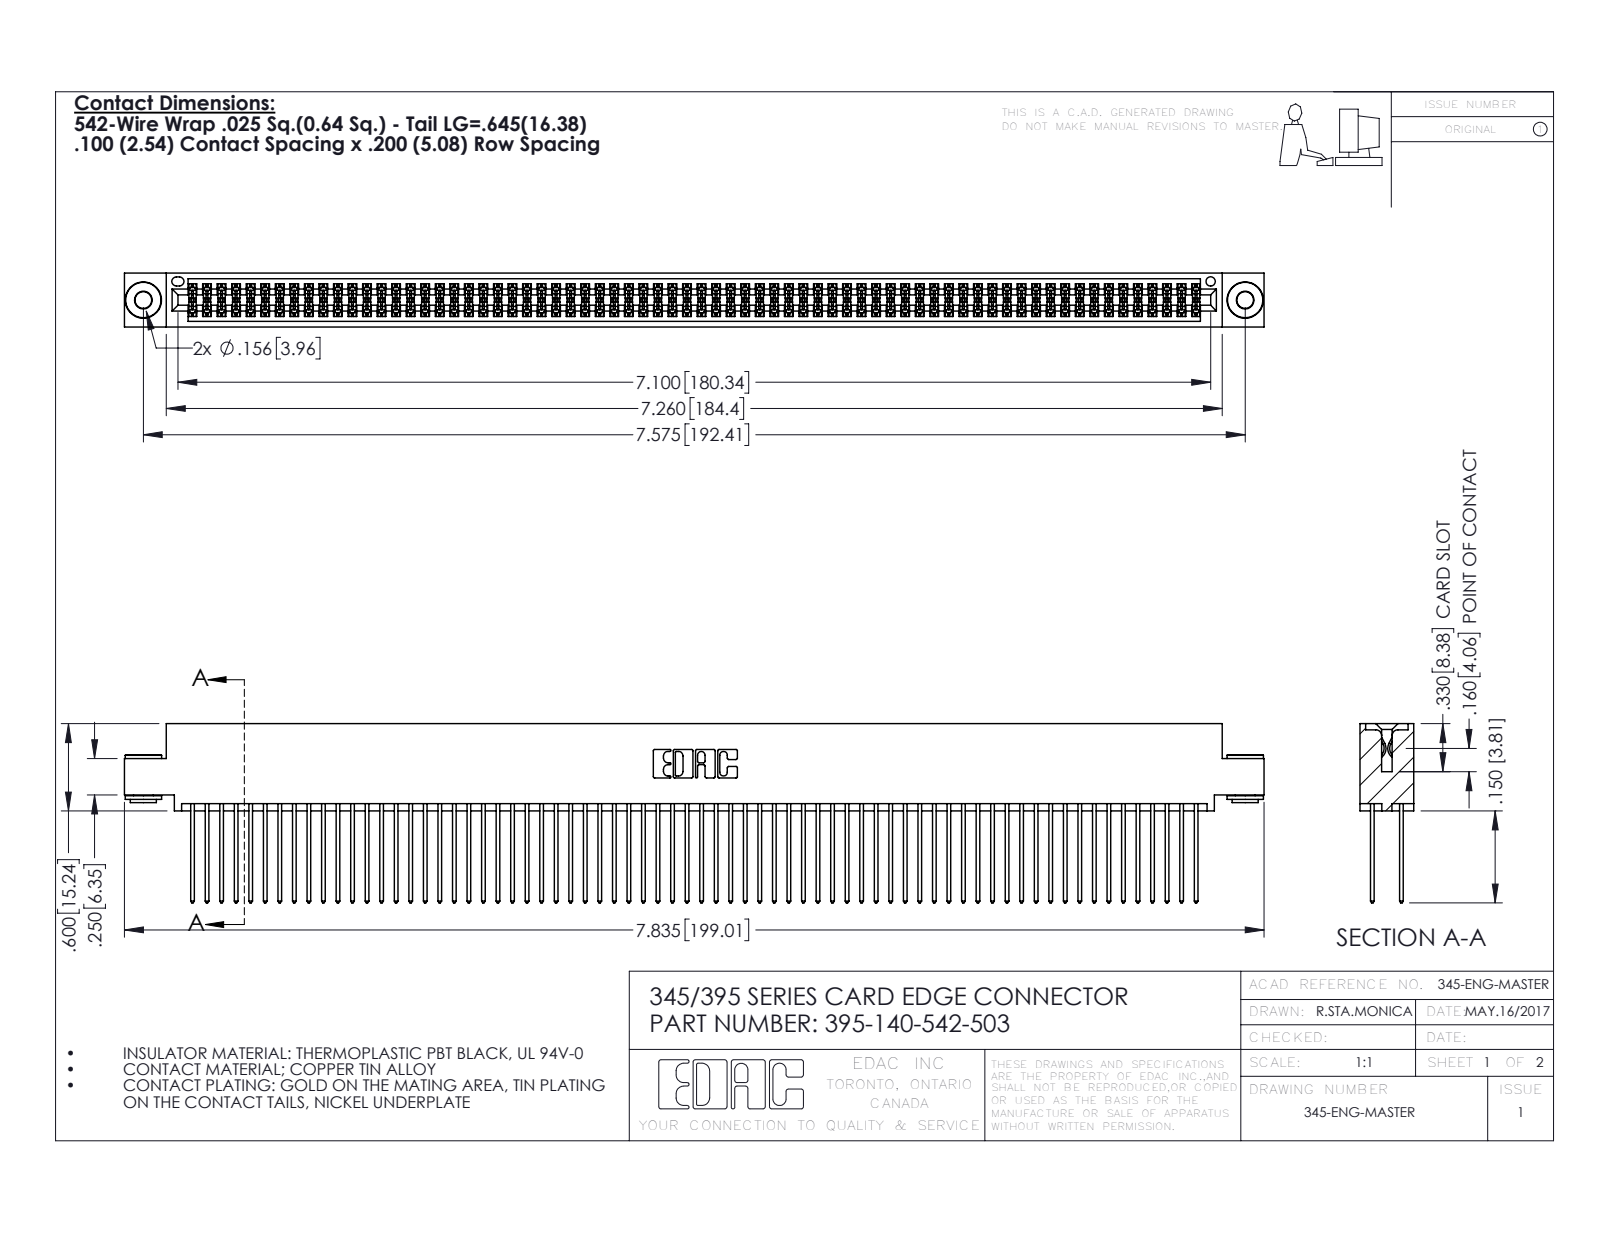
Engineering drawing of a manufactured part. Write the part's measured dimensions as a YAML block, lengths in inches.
part_name: "345-292-001_345-293-142; 345 Part_0.110 Offset - 0.156 Dia-TH; 345-250-002_345-250-002-102; 395-140-542-503"
step_written_by: "SolidWorks 2016 (CONFIG_CONTROL_DESIGN)"
units: inches
bodies: {solids: 143, faces: 7168, planar: 4714, cylindrical: 2446, other: 8}
overall_size: [7.835, 1.232, 0.37]
volume: 1.232
surface_area: 52.29
round_holes:
  - {diameter: 0.116, count: 2}
  - {diameter: 0.156, count: 2}
  - {diameter: 0.064, count: 1}
round_bosses_or_shafts:
  - {diameter: 0.25, count: 2}
  - {diameter: 0.18, count: 2}
  - {diameter: 0.136, count: 2}
partial_cylinders:
  - {radius: 0.006, count: 210}
  - {radius: 0.01, count: 140}
  - {radius: 0.01, count: 22}
  - {radius: 0.007, count: 6}
  - {radius: 0.031, count: 6}
  - {radius: 0.026, count: 3}
  - {radius: 0.014, count: 2}
  - {radius: 0.019, count: 2}
face_to_face_distances: [0.072, 0.298, 0.2, 0.025, 0.098, 0.272, 0.225, 0.37, 0.175, 0.149]
hole_center_spacings: [0.27, 7.339, 7.575]
